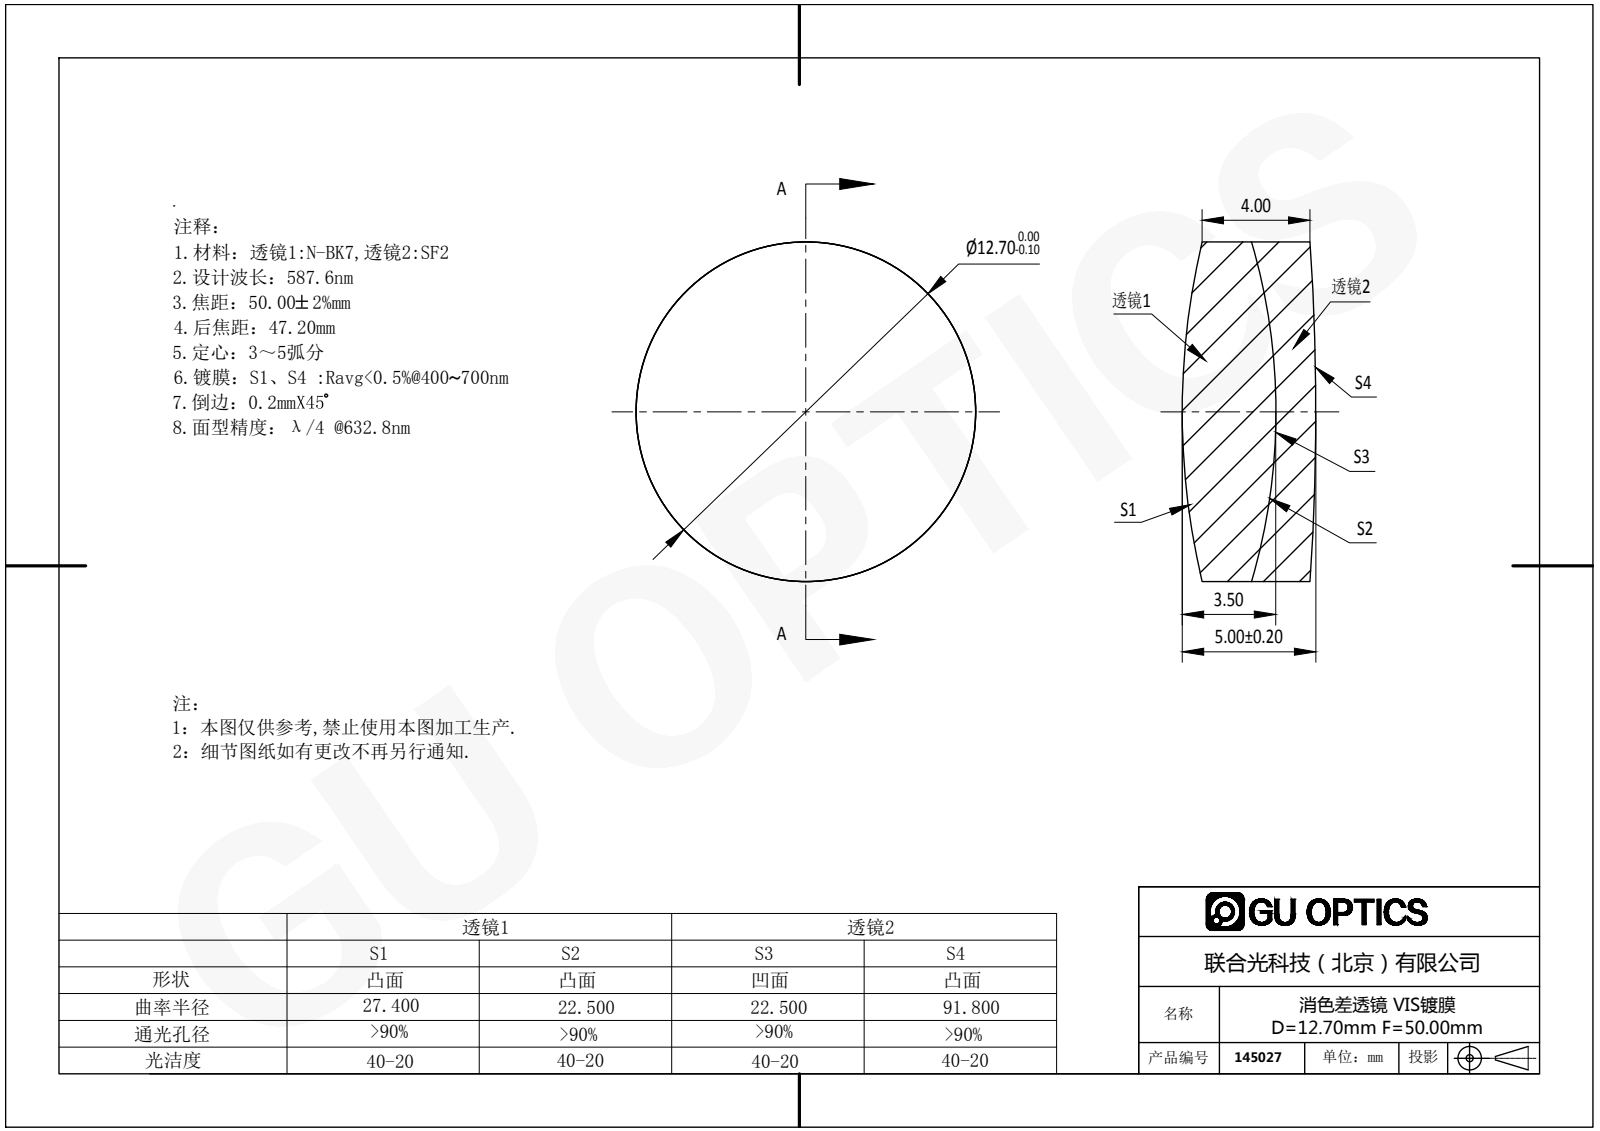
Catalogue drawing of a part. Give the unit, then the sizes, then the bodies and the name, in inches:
Units: inches
Overall size (bounding box): 0.5 × 0.5 × 0.197
Round bosses / shafts (diameter × count): ⌀0.5 ×1
Volume: 0.035 in³ · Surface area: 1.05 in²
Bodies: 2 solids, 12 faces (0 planar, 4 cylindrical, 8 other)
Part name (STEP PRODUCT): 145027
STEP written by: SolidWorks 2016 (AUTOMOTIVE_DESIGN)
